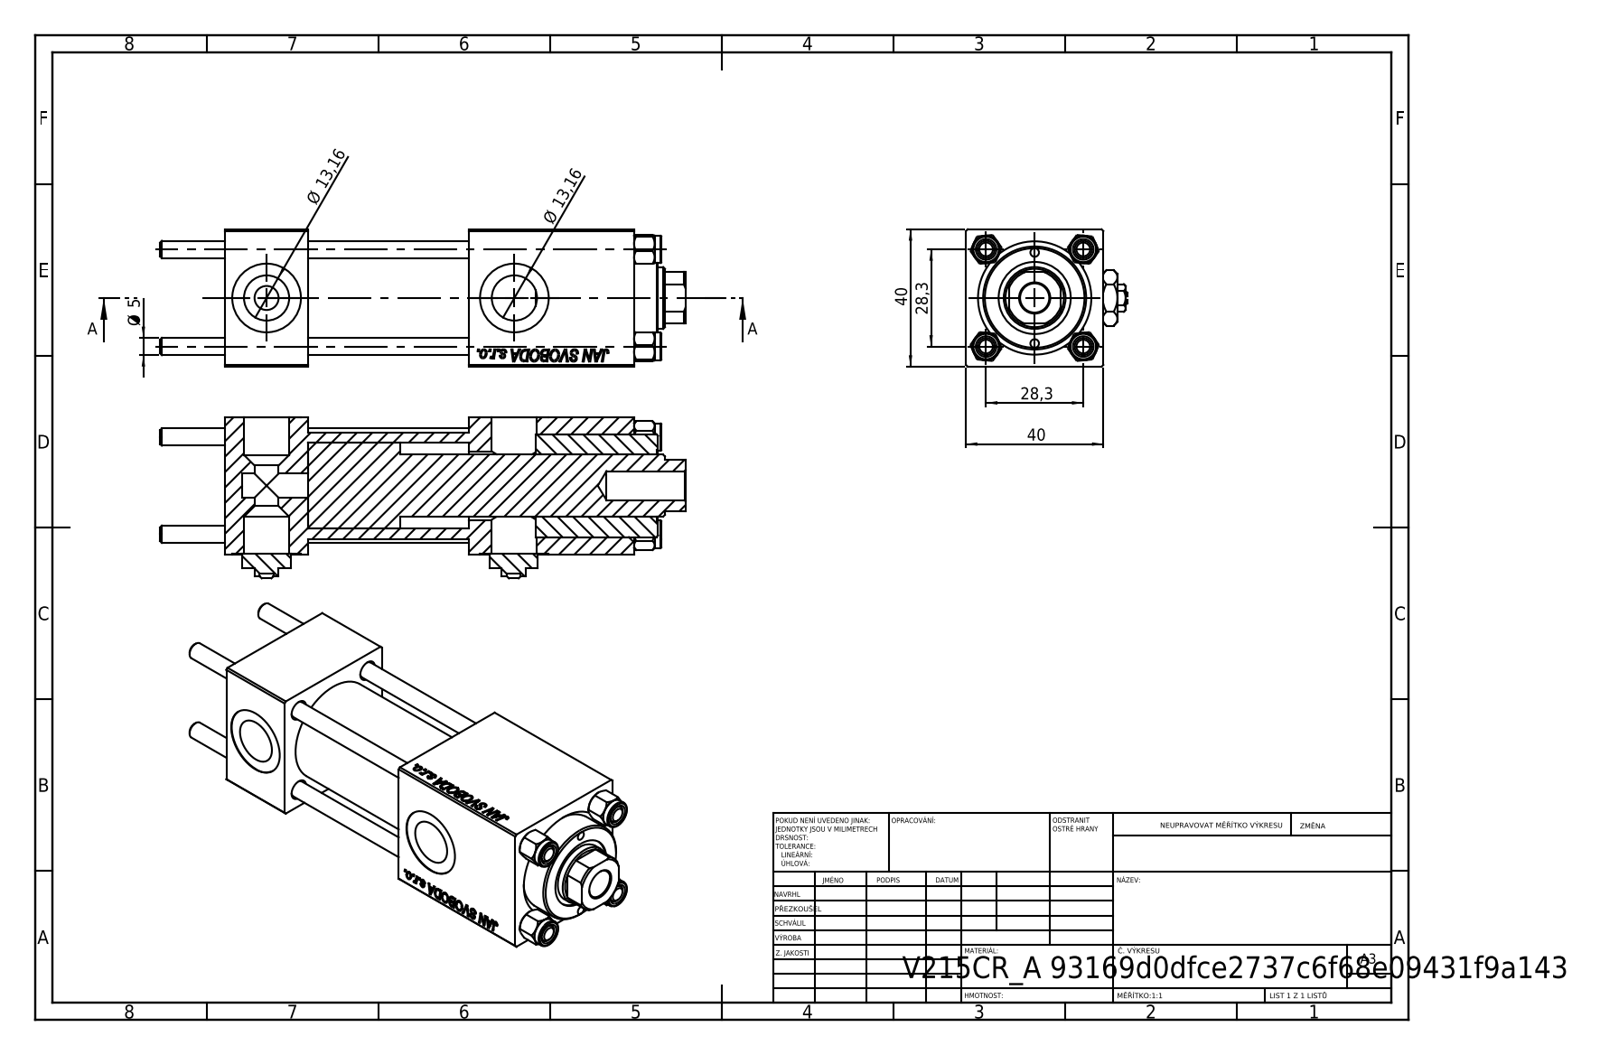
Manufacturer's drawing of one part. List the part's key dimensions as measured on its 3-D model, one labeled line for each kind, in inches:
Part name (STEP PRODUCT): CR025_012_A_0_G_A_G_M_020_+#_##_TYCINKA; V215CR_BODY_A; NUT_M5; V215_VC_A (+2 more)
STEP written by: SolidWorks 2019 (CONFIG_CONTROL_DESIGN)
Units: inches
Bodies: 13 solids, 1235 faces (565 planar, 92 cylindrical, 578 other)
Overall size (bounding box): 6.024 × 1.85 × 1.575
Volume: 9.187 in³ · Surface area: 97.89 in²
Round holes (diameter × count): ⌀0.197 ×4, ⌀0.787 ×4, ⌀0.518 ×3, ⌀0.098 ×2, ⌀0.276 ×2, ⌀0.335 ×1, ⌀0.512 ×1, ⌀0.709 ×1, ⌀0.827 ×1, ⌀0.984 ×1, ⌀1.181 ×1
Round bosses / shafts (diameter × count): ⌀0.315 ×4, ⌀1.22 ×1
Partial cylindrical surfaces — rounded edges, fillets, slot ends (radius × count): R0.335 ×1
Main face-to-face distances: 1.575, 0.945, 1.567, 1.85, 2.795, 3.555, 2.61, 0.76, 3.74, 4.685
Hole centre spacings: 0.558, 0.788, 1.114, 1.214, 0.522, 1.576, 1.043, 2.835
